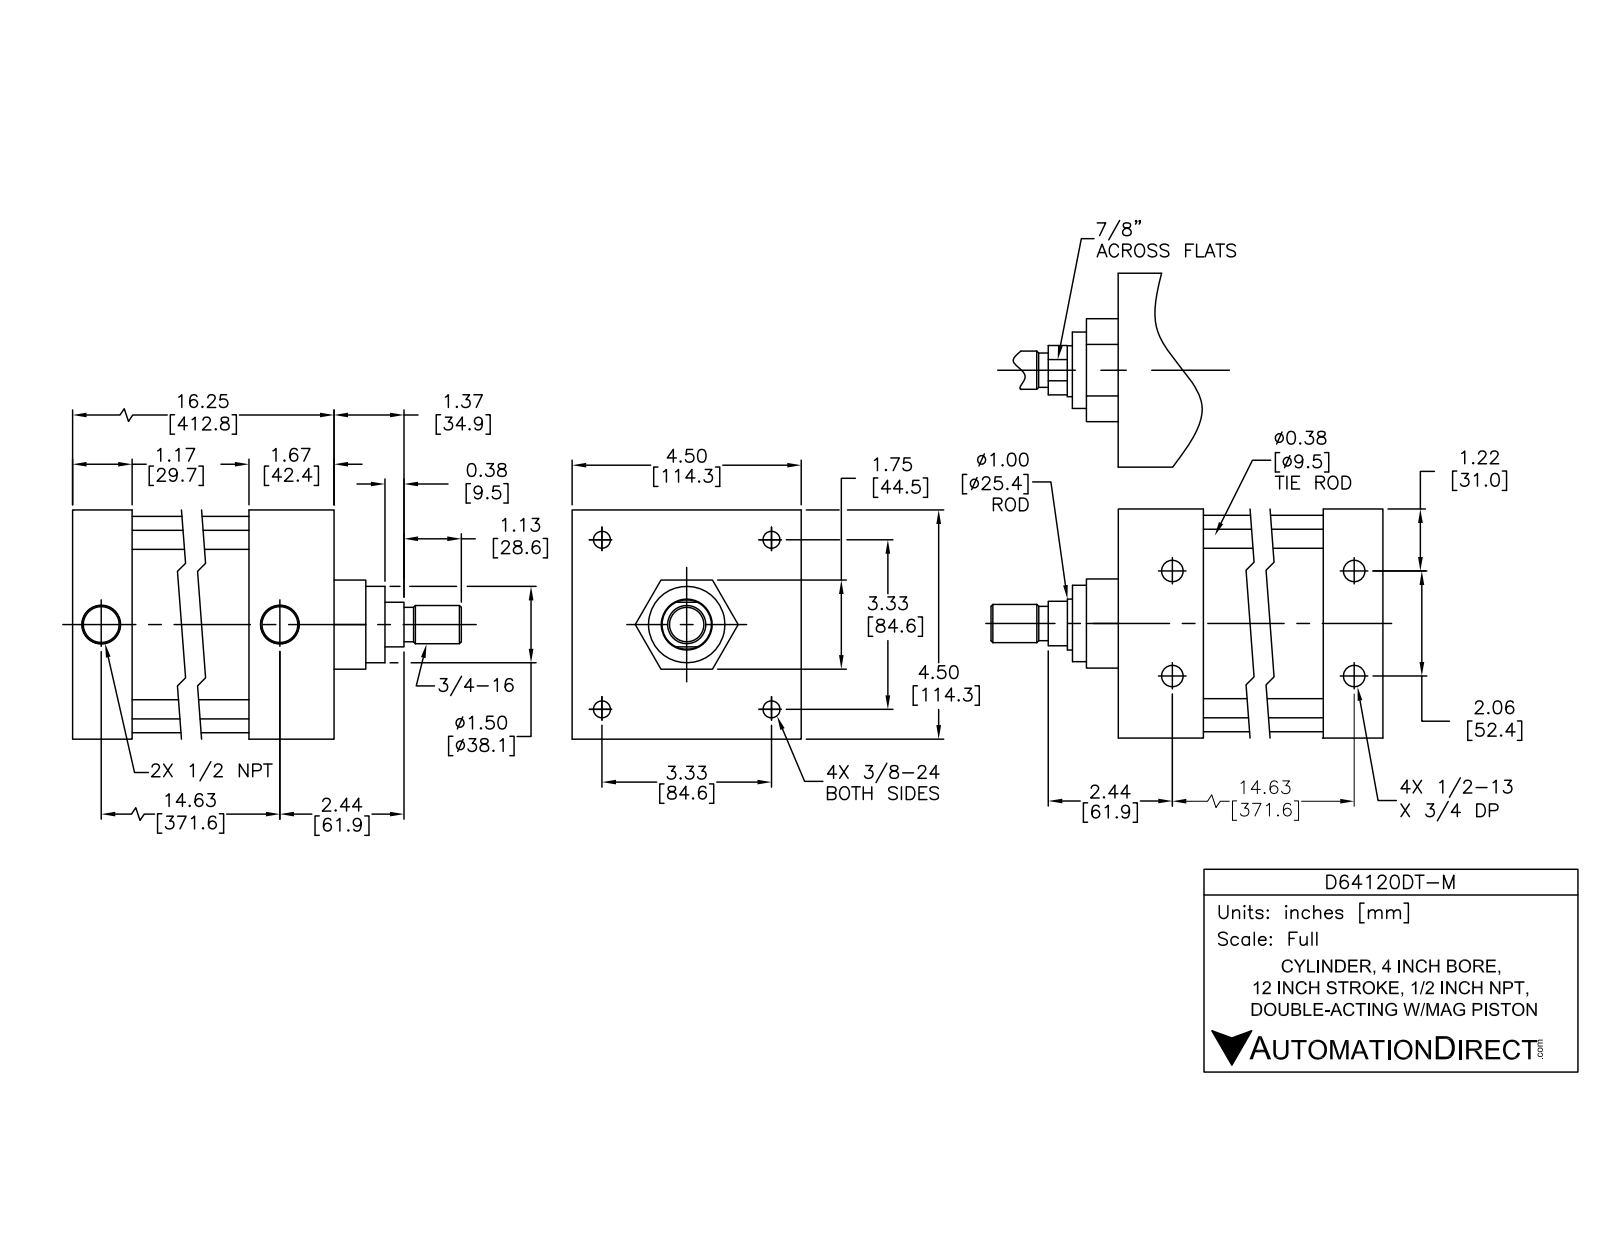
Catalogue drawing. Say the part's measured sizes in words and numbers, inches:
The part is named "D64120DT-M; D64120DT-M PISTON; D64120DT-M BODY". Its 3-D file was written by "SolidWorks 2015 (AUTOMOTIVE_DESIGN)". It is 12 solids with 303 faces: 99 planar, 114 cylindrical and 90 other. Overall it measures 18.745 by 4.5 by 4.5 inches. Its volume is 110.5 cubic inches and its surface area 690.2 square inches. Round holes: 4 of diameter 0.33, 4 of diameter 0.406, 4 of diameter 0.417, 4 of diameter 0.625, 2 of diameter 0.5, 2 of diameter 0.766, 1 of diameter 1, 1 of diameter 1.003, 1 of diameter 4. Round bosses or shafts: 4 of diameter 0.609, 4 of diameter 0.375, 4 of diameter 0.34, 1 of diameter 4.25, 1 of diameter 3.997, 1 of diameter 1.75, 1 of diameter 0.997, 1 of diameter 0.97. Partial cylindrical surfaces (rounded edges, fillets, slot ends): 4 of radius 0.45. The main face-to-face distances are 4.5, 0.08, 13.326, 16.246, 1.75, 14.997, 1.249, 13.751, 1.246, 2.495. The hole center spacings are 1.031, 14.658, 14.622, 2.062, 2.349, 2.349, 3.322, 3.322.
